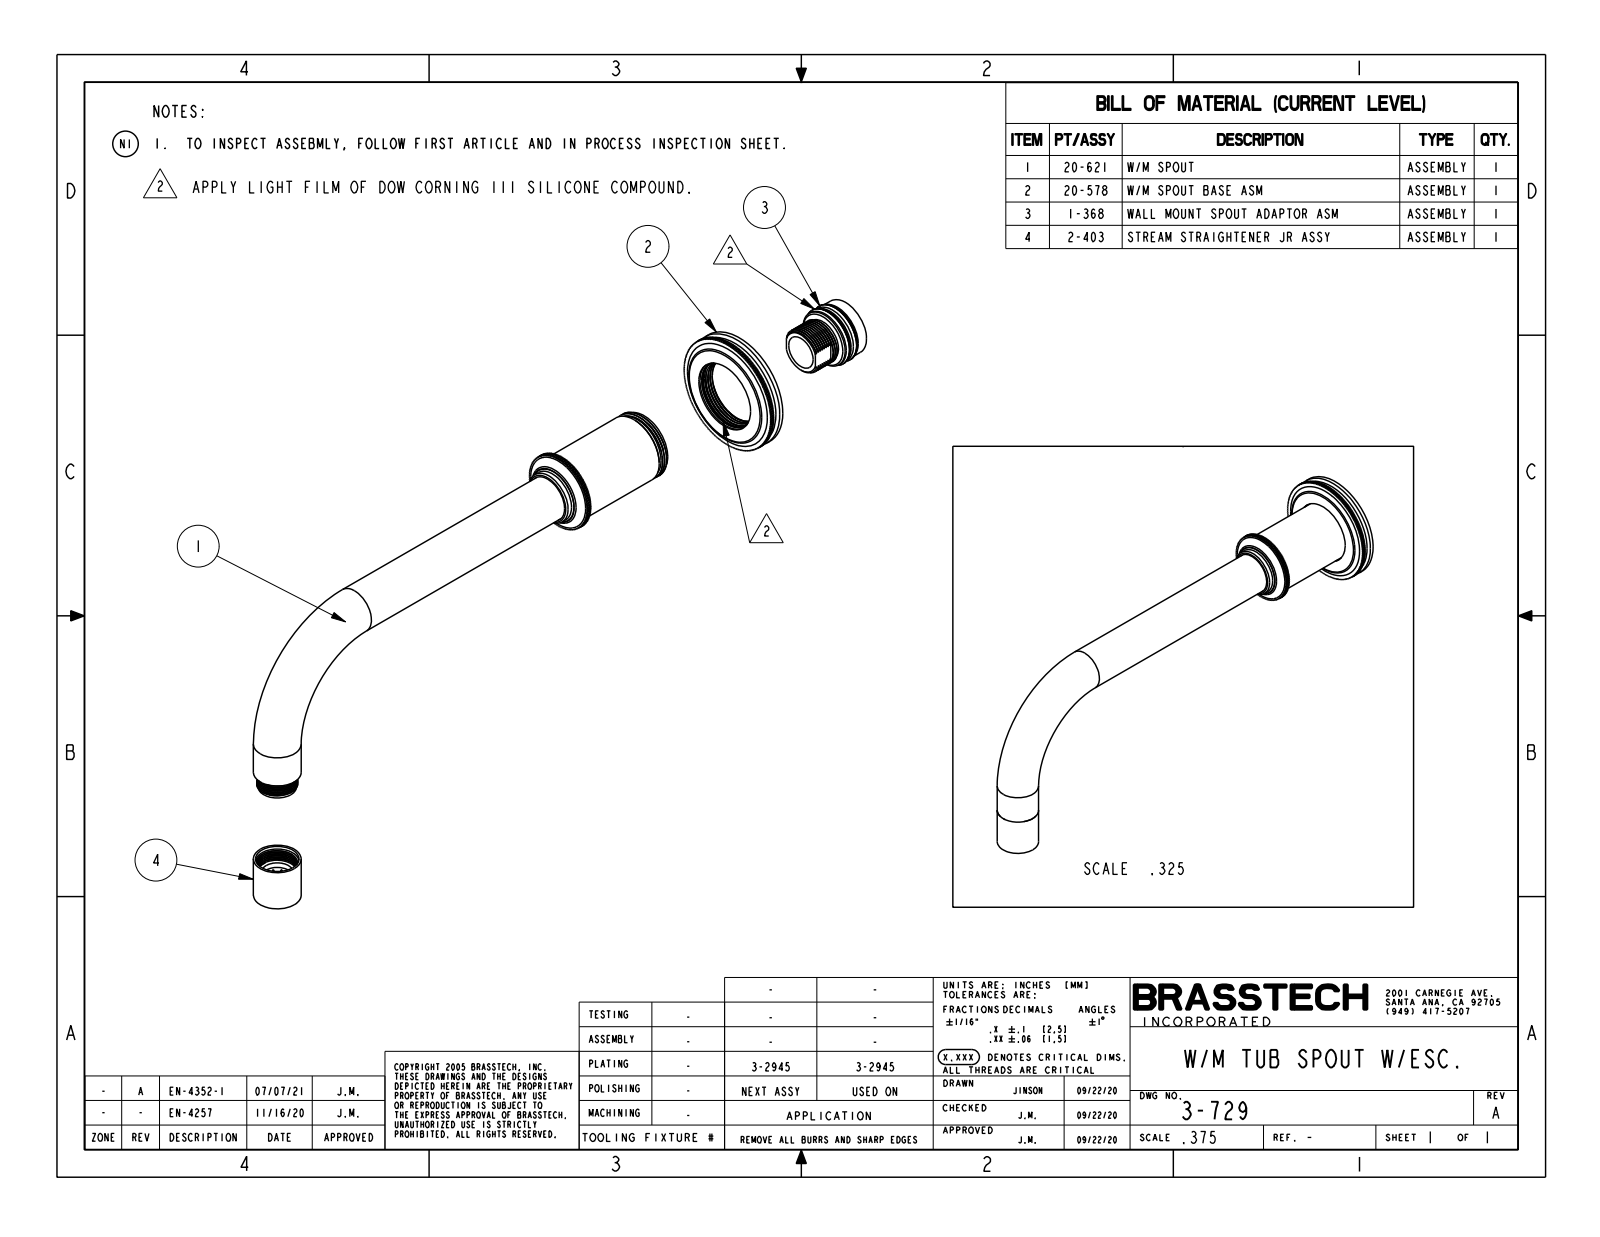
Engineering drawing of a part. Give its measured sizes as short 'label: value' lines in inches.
name: 3-729
written by: CREO PARAMETRIC BY PTC INC, 2019352 (CONFIG_CONTROL_DESIGN)
unit: in
bodies: 1 solid, 330 faces (202 planar, 112 cylindrical, 16 other)
size: 9.938 × 4.565 × 2.25
volume: 9.936 in³; area: 46.28 in²
holes: 1× ⌀0.691
bosses: 2× ⌀0.875, 1× ⌀2.25, 1× ⌀2.15, 1× ⌀1.312, 1× ⌀1
rounds: 1× R0.75
face distances: 0.38, 0.31, 0.07, 2.125, 1.815, 1.745, 0.15, 0.23, 0.08, 1.895
